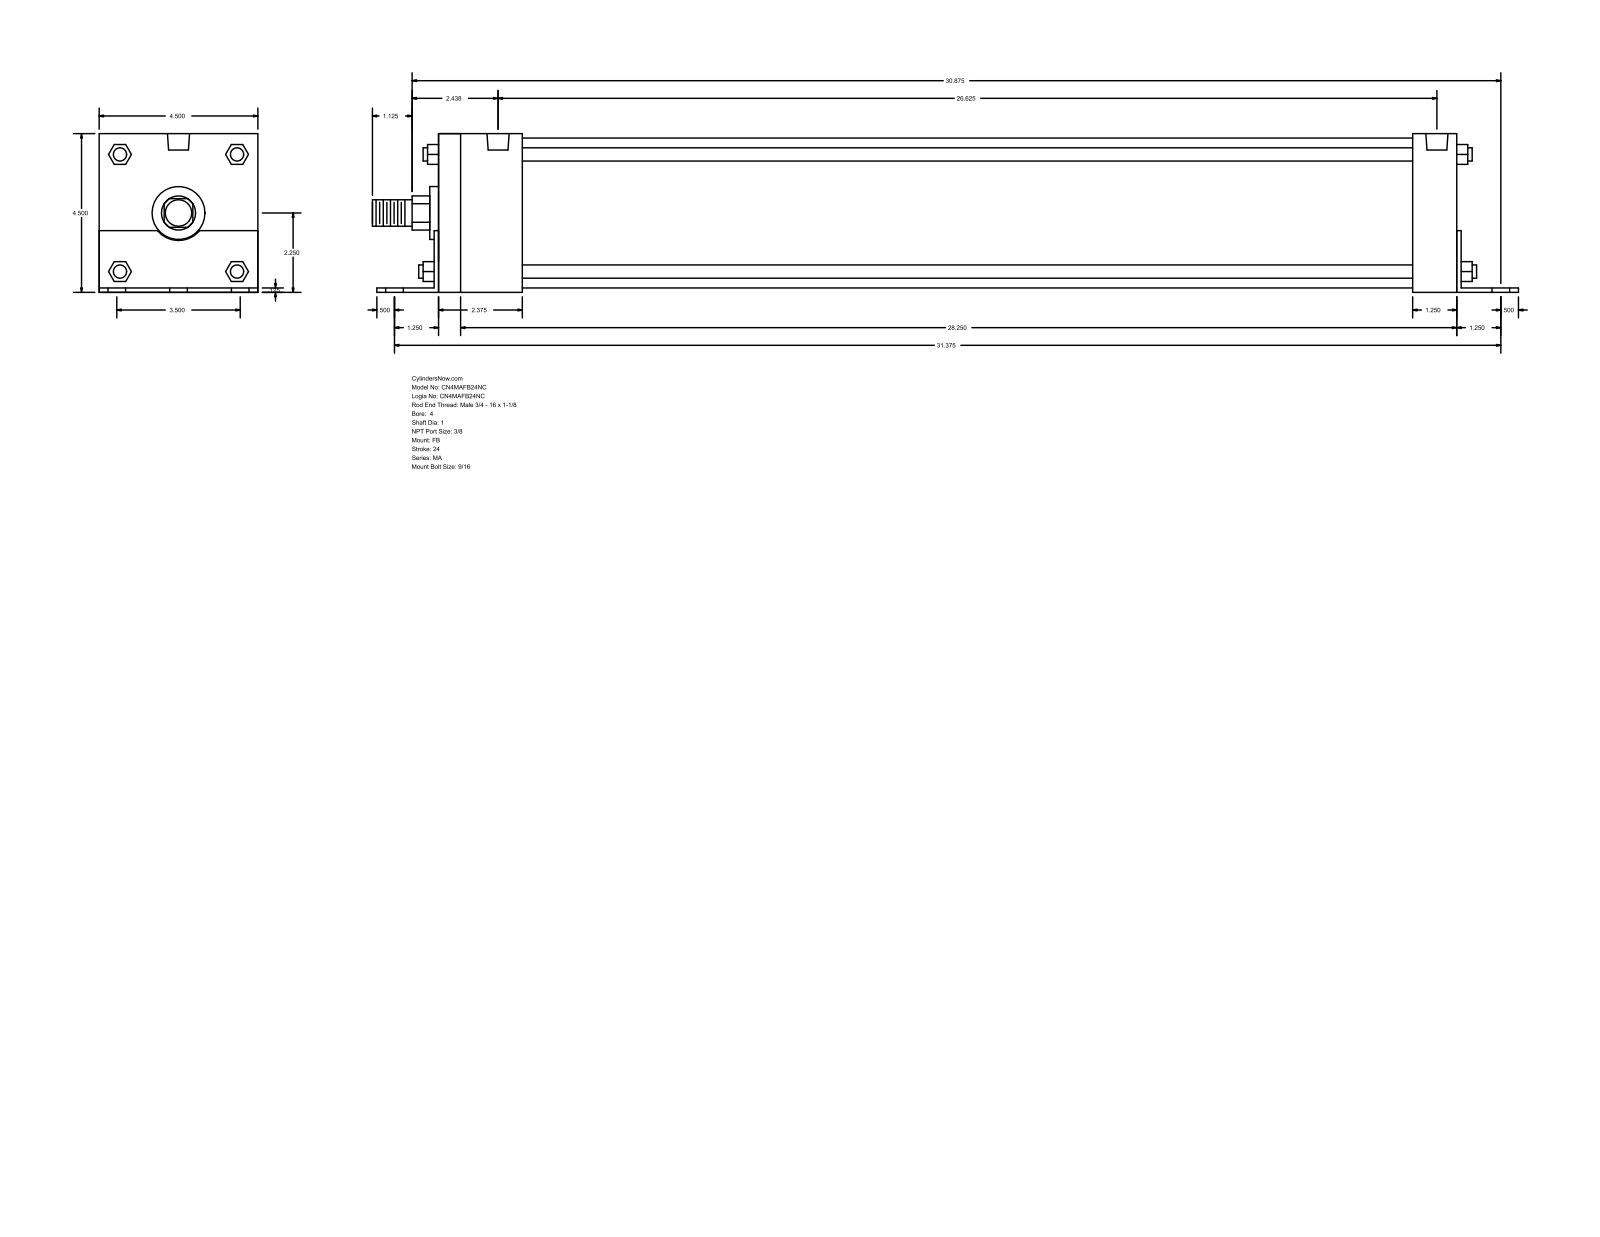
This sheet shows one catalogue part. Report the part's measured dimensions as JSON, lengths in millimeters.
{"part_name": "MA_FB__0400_1", "step_written_by": "GSSL Pune (CONFIG_CONTROL_DESIGN)", "units": "millimeters", "bodies": {"solids": 0, "faces": 140, "planar": 105, "cylindrical": 35, "other": 0}, "overall_size": [825.5, 114.35, 114.3], "round_holes": [[14.29, 6], [11.11, 4], [15.93, 2]], "round_bosses_or_shafts": [[9.53, 4], [107.95, 1], [38.1, 1], [25.4, 1], [19.05, 1]], "partial_cylinders_radius": [[12.29, 1], [19.81, 1]], "face_to_face_distances": [114.3, 3.17, 114.35, 736.6, 3.12, 111.18, 733.43, 739.77, 704.85, 701.68], "hole_center_spacings": [44.45, 798.17, 796.93, 64, 67.51, 86.85, 88.9, 90.97]}
